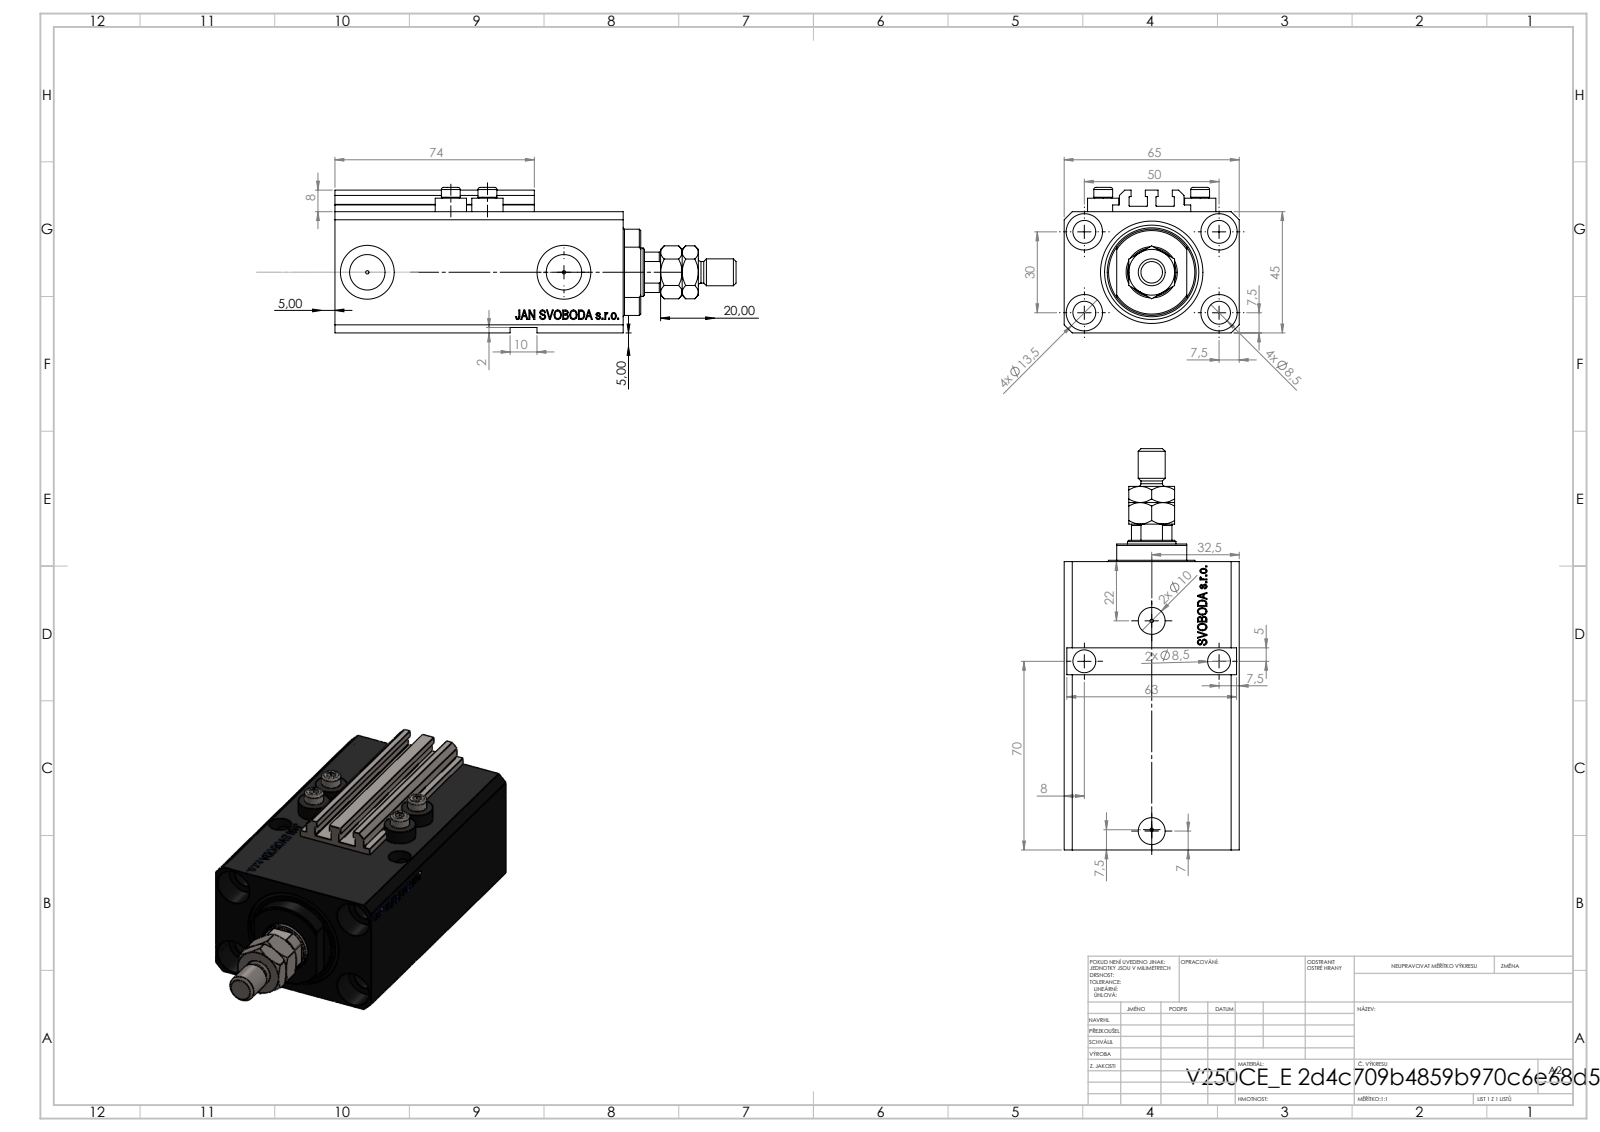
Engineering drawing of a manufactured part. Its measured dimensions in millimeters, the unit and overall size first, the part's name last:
Units: millimetres
Overall size (bounding box): 149 × 65 × 54
Round holes (diameter × count): ⌀8.5 ×9, ⌀1.25 ×4, ⌀4 ×4, ⌀13.5 ×4, ⌀10 ×2, ⌀13.16 ×2, ⌀20 ×2, ⌀18 ×1, ⌀25 ×1, ⌀38 ×1
Round bosses / shafts (diameter × count): ⌀11.6 ×4, ⌀7 ×4, ⌀10 ×1, ⌀8 ×1
Partial cylindrical surfaces — rounded edges, fillets, slot ends (radius × count): R0.2 ×10, R8.5 ×1, R16 ×1
Main face-to-face distances: 45, 65, 14, 93, 2, 47, 107, 6.9, 20.5, 2.5
Hole centre spacings: 29.15, 50, 13.6, 14.76, 15.12, 27.51, 27.89, 30
Volume: 277 886 mm³ · Surface area: 78 614 mm²
Bodies: 9 solids, 1136 faces (526 planar, 150 cylindrical, 460 other)
Part name (STEP PRODUCT): V250CE_VC_E; MTA; ALLEN BOLT V250CE; V250CE_E_Body (+1 more)
STEP written by: SolidWorks 2019 (CONFIG_CONTROL_DESIGN)
